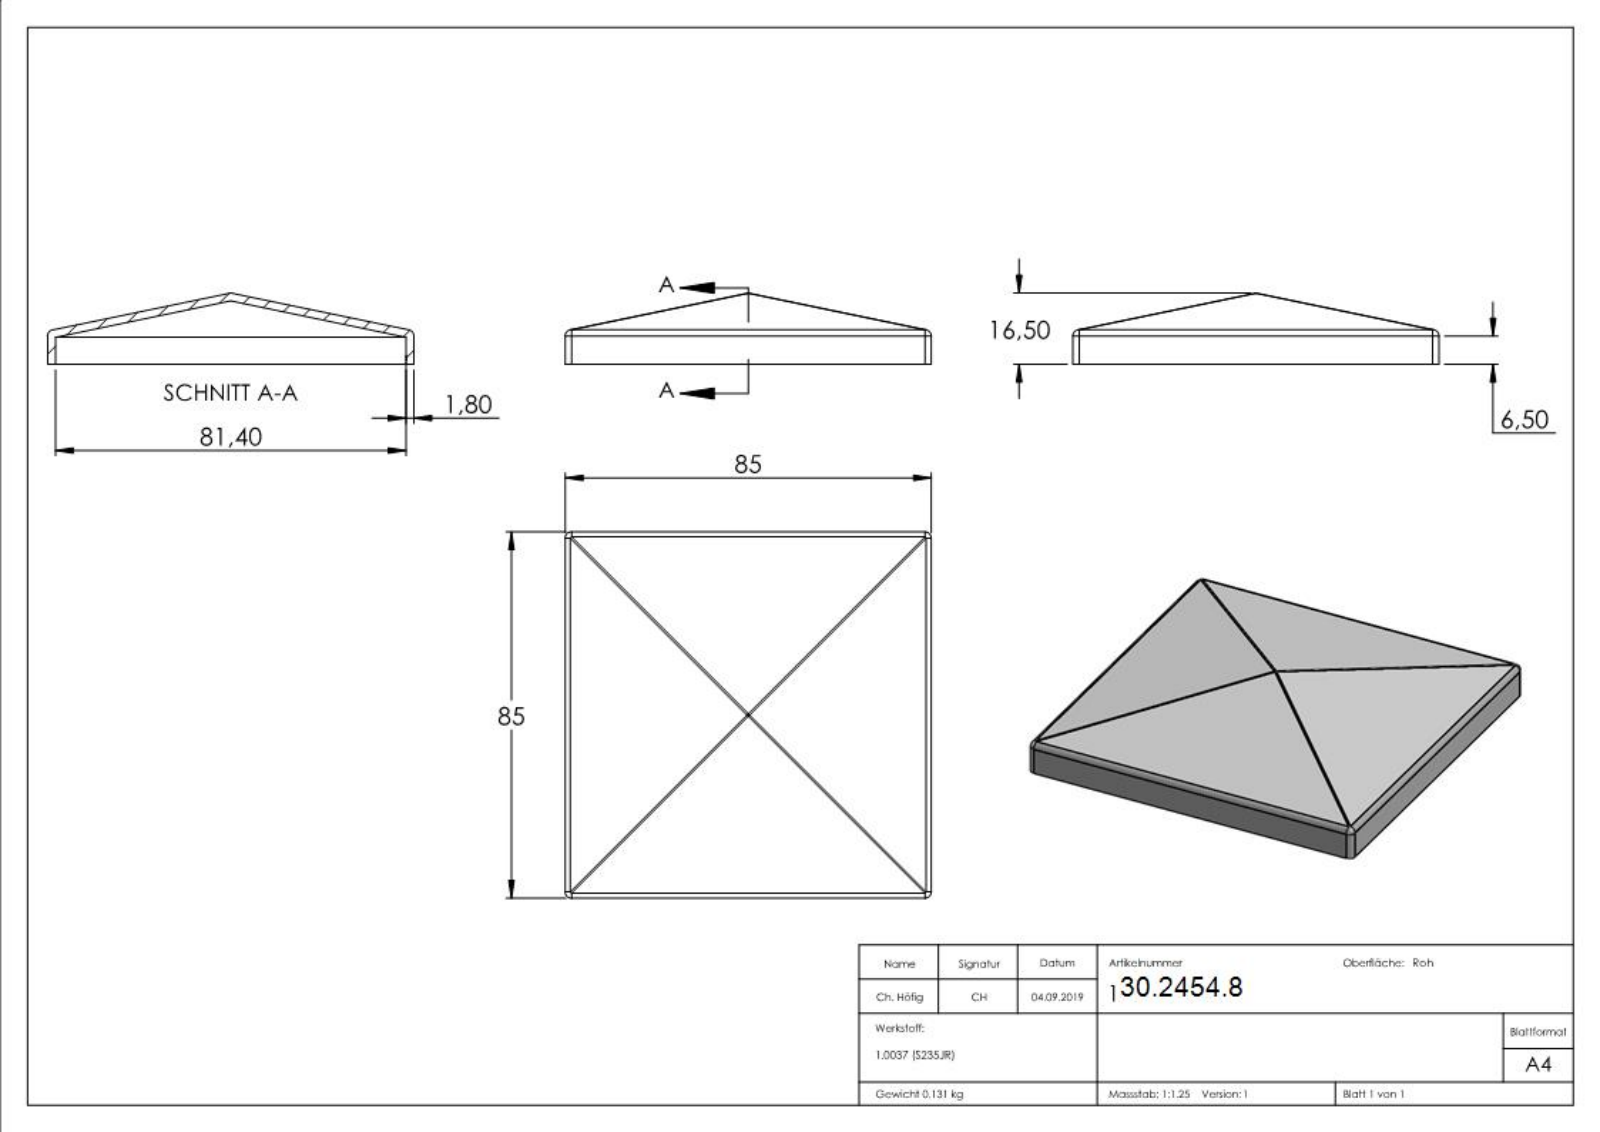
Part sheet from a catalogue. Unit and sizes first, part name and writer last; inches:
Units: inches
Overall size (bounding box): 3.346 × 3.346 × 0.65
Partial cylindrical surfaces — rounded edges, fillets, slot ends (radius × count): R0.059 ×12
Main face-to-face distances: 0.07, 0.071, 3.276, 3.346, 3.205, 0.067, 3.209, 3.28, 0.015, 0.08
Volume: 1.025 in³ · Surface area: 29.85 in²
Bodies: 1 solid, 222 faces (111 planar, 12 cylindrical, 99 other)
Part name (STEP PRODUCT): 165-80
STEP written by: SolidWorks 2015 (CONFIG_CONTROL_DESIGN)
